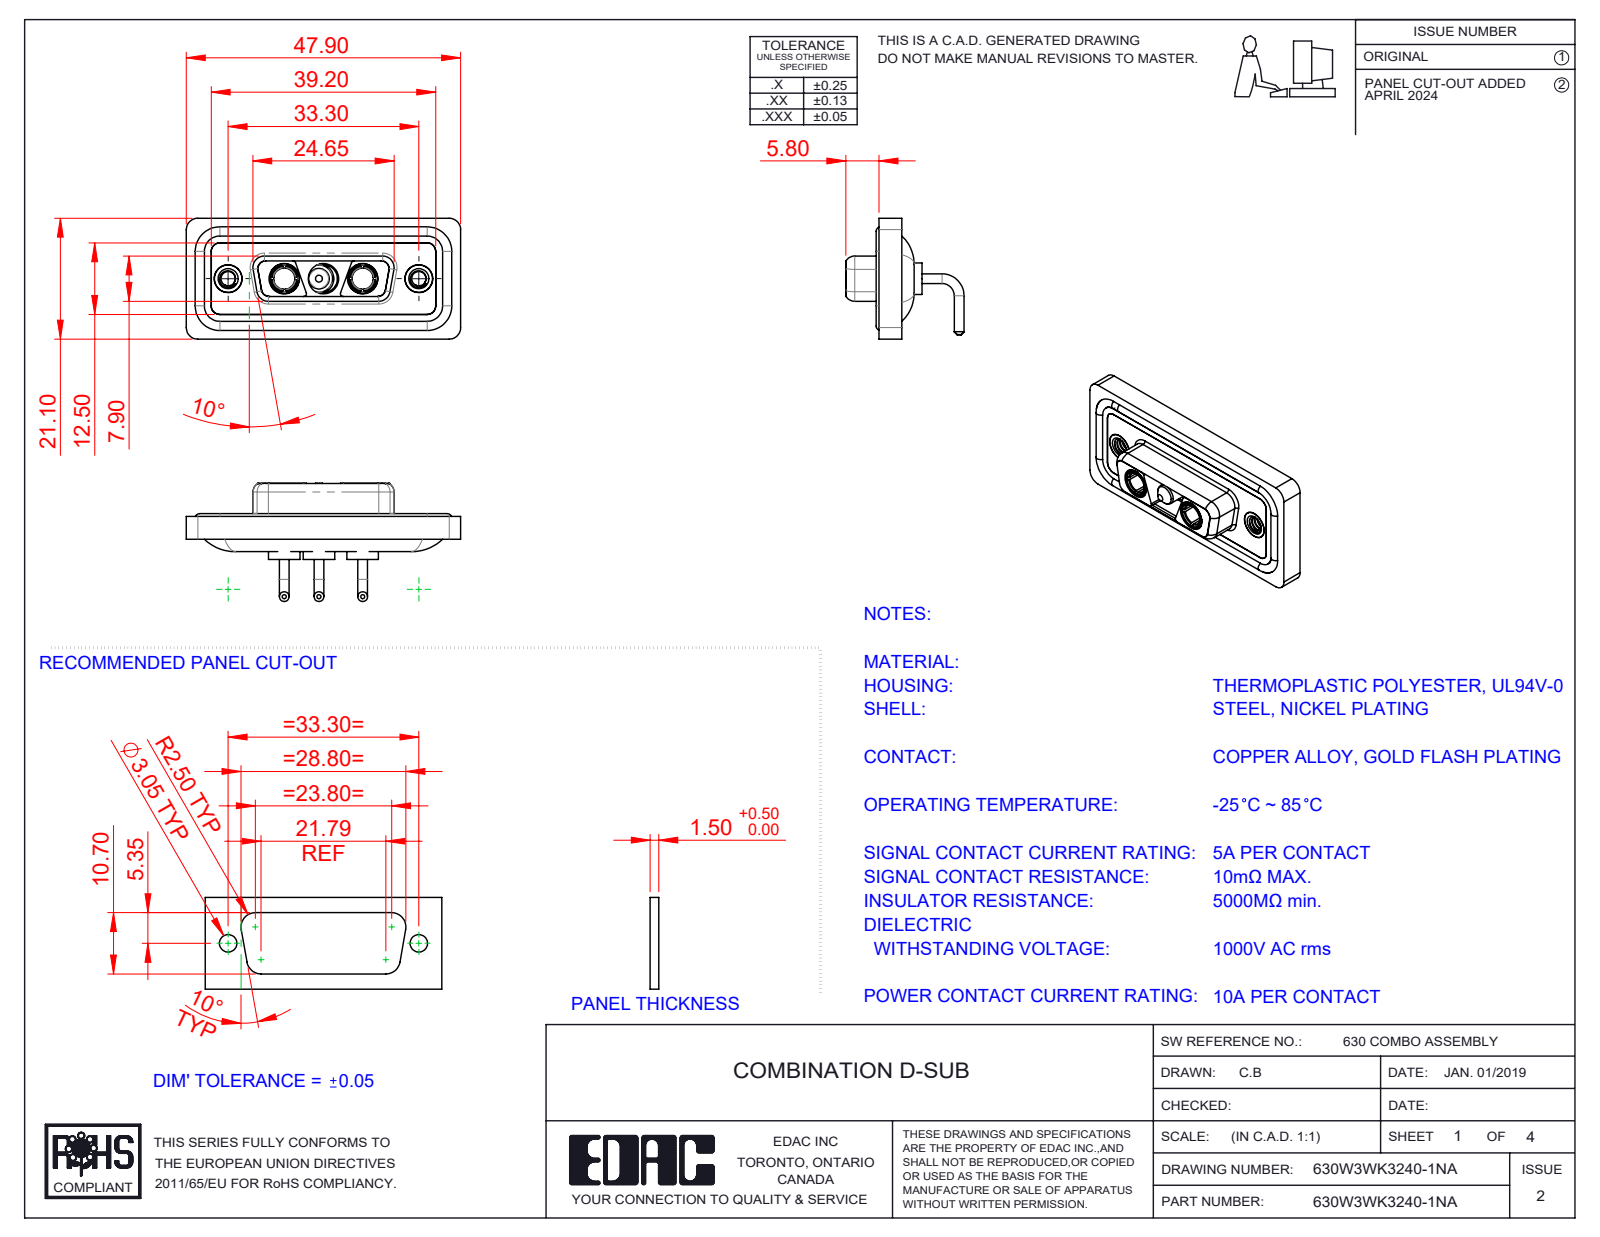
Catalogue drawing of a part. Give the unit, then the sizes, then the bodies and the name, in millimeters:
Units: millimetres
Overall size (bounding box): 47.9 × 21.1 × 20.65
Round holes (diameter × count): ⌀4.85 ×5, ⌀5.3 ×3, ⌀2.5 ×2, ⌀3.7 ×2, ⌀4 ×2, ⌀4.05 ×2, ⌀5 ×2
Round bosses / shafts (diameter × count): ⌀1.7 ×6, ⌀1.6 ×4, ⌀5.5 ×3, ⌀5.2 ×3, ⌀4.75 ×3, ⌀3.75 ×3, ⌀4.96 ×2, ⌀4.95 ×2
Partial cylindrical surfaces — rounded edges, fillets, slot ends (radius × count): R2 ×20, R1.5 ×18, R1.35 ×12, R0.5 ×8, R1.6 ×8, R0.25 ×4, R0.6 ×4, R0.65 ×4
Main face-to-face distances: 0.4, 1.8, 1.1, 1.6, 2.9, 2.5, 3.1, 3.7, 1.5, 4.1
Hole centre spacings: 6.85, 9.8, 16.65, 23.5, 13.7, 33.3
Volume: 5 851 mm³ · Surface area: 9 589 mm²
Bodies: 13 solids, 589 faces (178 planar, 262 cylindrical, 149 other)
Part name (STEP PRODUCT): Power Pin_10A RA; 630Combo Housing_3WK3; 630Combo Shell Front_15 Contacts; 630W3WK3140-1NA (+4 more)
STEP written by: SolidWorks 2023 (CONFIG_CONTROL_DESIGN)
